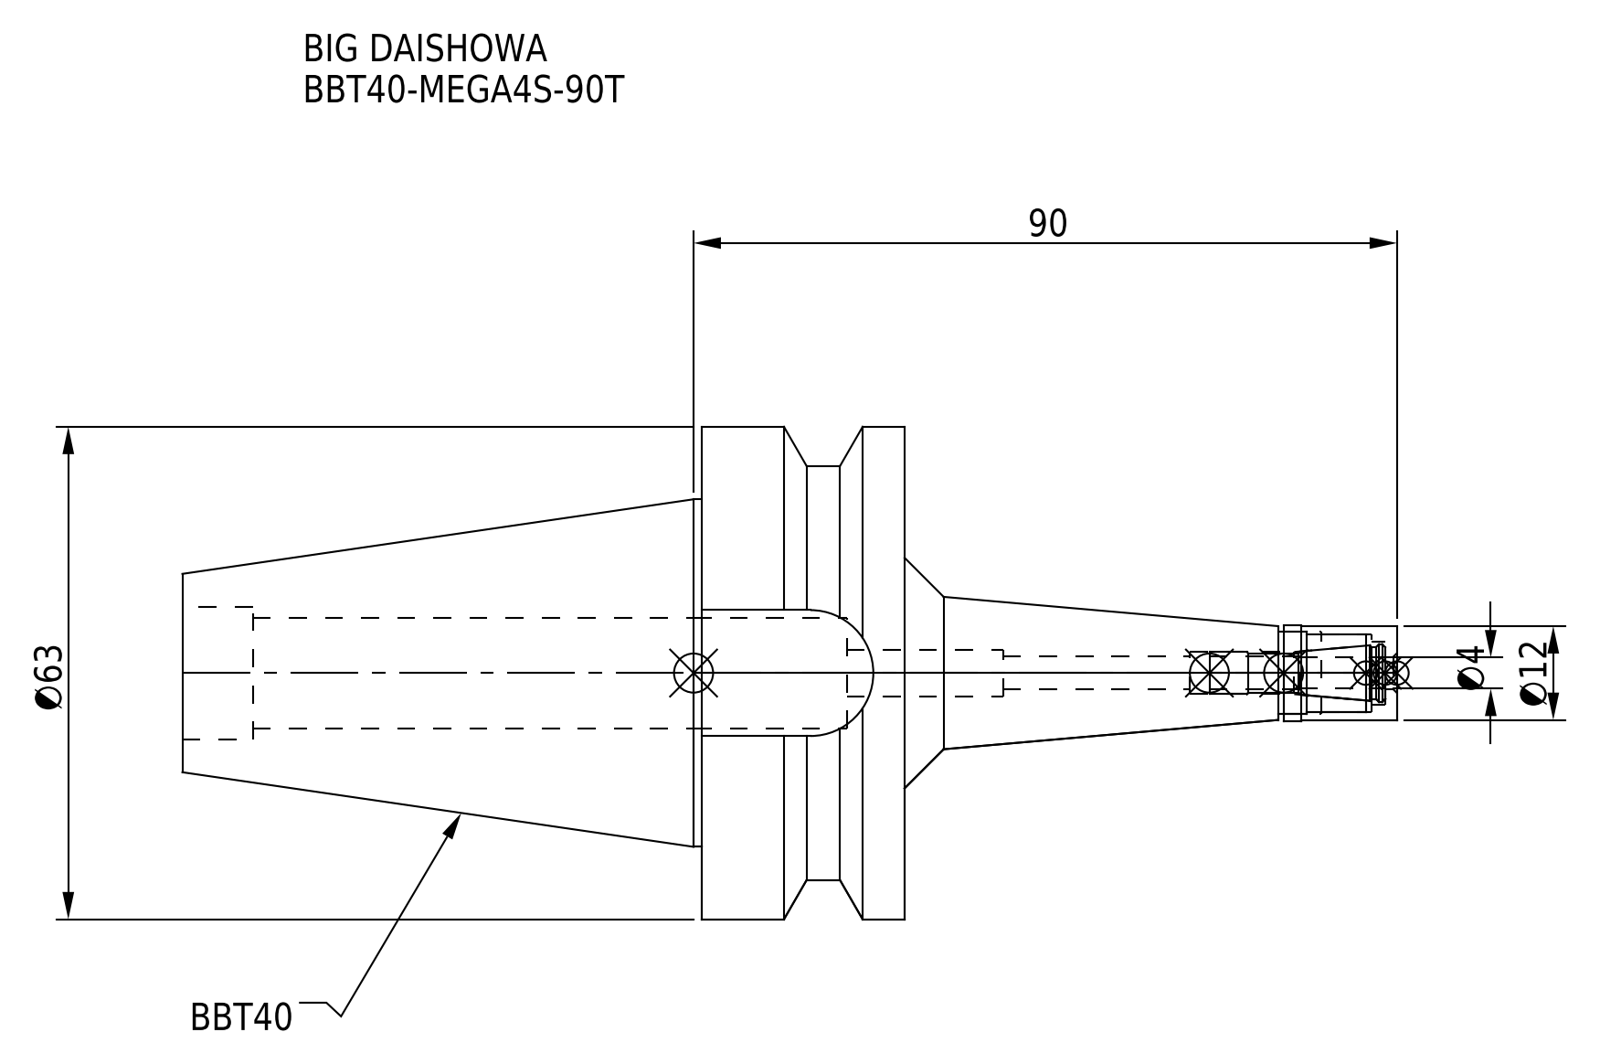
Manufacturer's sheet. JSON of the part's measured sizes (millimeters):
{"part_name": "BBT40-MEGA4S-90T-040.stp; BBT40-MEGA4S-90T-040-FreeParts; BBT40-MEGA4S-90T_1.stp; BBT40-MEGA4S-90T (+3 more)", "step_written_by": "SolidWorks 2019 (CONFIG_CONTROL_DESIGN)", "units": "millimeters", "bodies": {"solids": 2, "faces": 74, "planar": 22, "cylindrical": 38, "other": 14}, "overall_size": [155.4, 63, 63], "volume_mm3": 132431, "surface_area_mm2": 27375, "round_holes": [[4.1, 1], [4.2, 1], [5.4, 1], [6, 1], [8, 1], [10, 1], [10.5, 1], [14.2, 1], [17, 1]], "round_bosses_or_shafts": [[63, 1], [53, 1], [44.45, 1], [12.3, 1], [12, 1]], "partial_cylinders_radius": [[8.05, 1]], "face_to_face_distances": [26, 45, 66.4, 92.4, 16.1, 85, 7.4, 18.6, 63, 70.4]}
